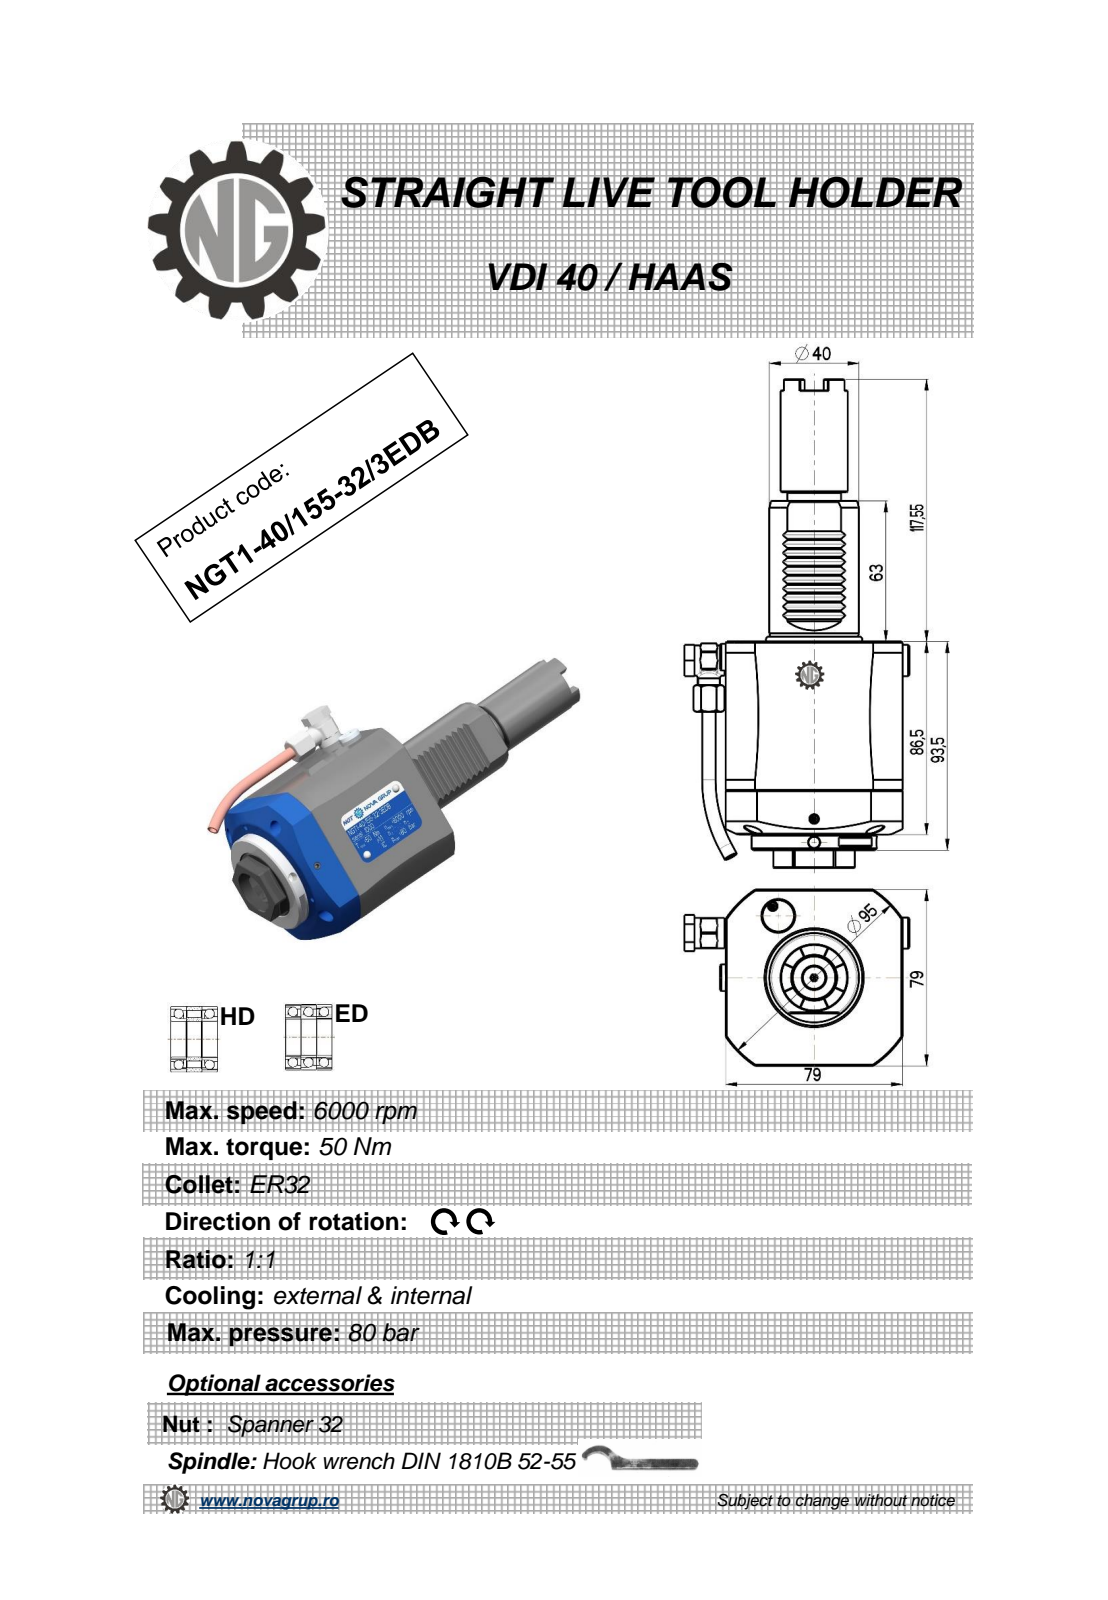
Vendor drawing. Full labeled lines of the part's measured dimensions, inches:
Part name (STEP PRODUCT): NGT1_40_155_32_3HDB
STEP written by: PRO/ENGINEER BY PARAMETRIC TECHNOLOGY CORPORATION, 2010280 (CONFIG_CONTROL_DESIGN)
Units: inches
Bodies: 2 solids, 413 faces (181 planar, 103 cylindrical, 129 other)
Overall size (bounding box): 8.624 × 3.953 × 3.11
Volume: 38.8 in³ · Surface area: 91.94 in²
Round holes (diameter × count): ⌀0.157 ×3, ⌀0.197 ×2, ⌀0.118 ×1, ⌀0.236 ×1, ⌀0.244 ×1, ⌀0.354 ×1, ⌀0.394 ×1, ⌀0.433 ×1, ⌀0.906 ×1
Round bosses / shafts (diameter × count): ⌀2.205 ×1, ⌀1.575 ×1, ⌀1.181 ×1, ⌀0.945 ×1, ⌀0.551 ×1, ⌀0.535 ×1, ⌀0.512 ×1, ⌀0.472 ×1
Partial cylindrical surfaces — rounded edges, fillets, slot ends (radius × count): R0.012 ×10, R0.016 ×6, R0.02 ×4, R0.303 ×1, R0.394 ×1, R1.85 ×1, R1.87 ×1
Main face-to-face distances: 3.11, 3.406, 0.276, 3.681, 0.111, 0.925, 2.185, 6.161, 5.886, 2.48
Hole centre spacings: 0.016, 2.011, 2.026, 3.304
